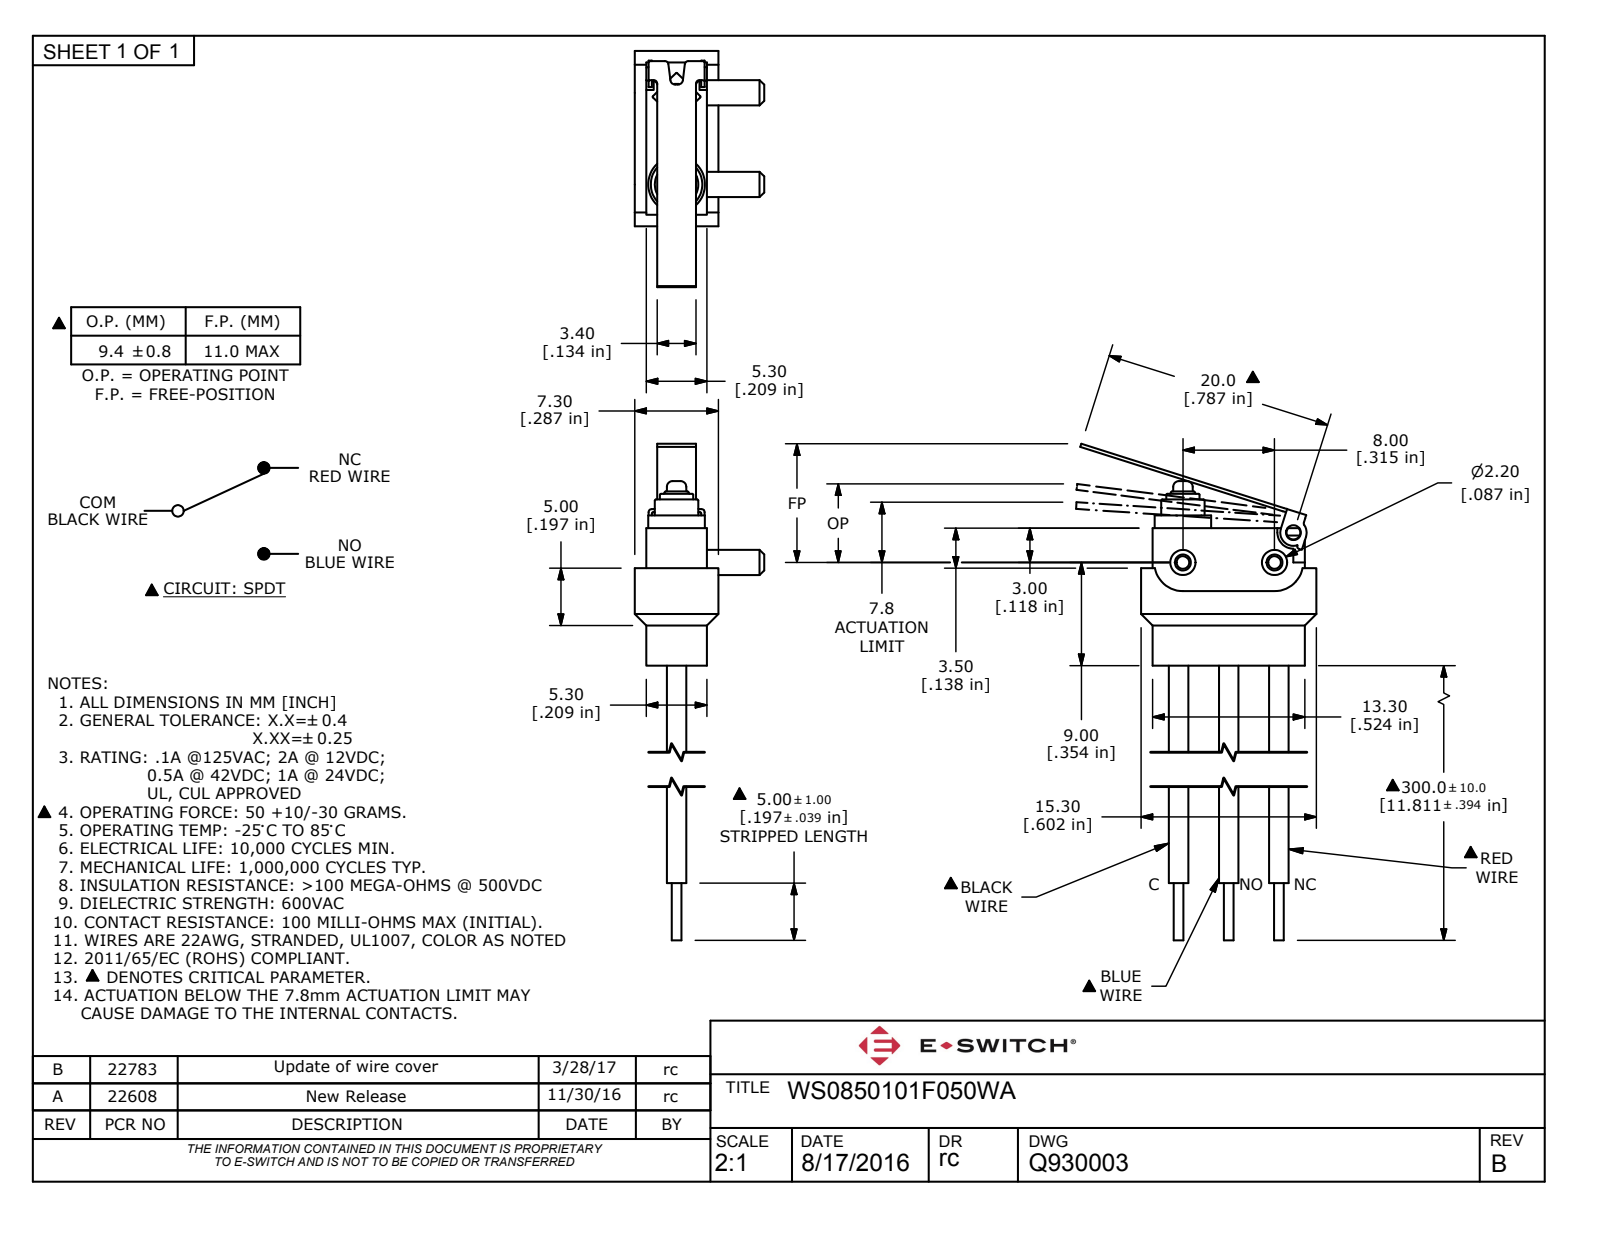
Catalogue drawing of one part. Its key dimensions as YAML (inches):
part_name: "WS0850101F050WA"
step_written_by: "Autodesk Inventor 2012 (CONFIG_CONTROL_DESIGN)"
units: inches
bodies: {solids: 2, faces: 284, planar: 164, cylindrical: 90, other: 30}
overall_size: [12.573, 0.811, 0.445]
volume: 0.178
surface_area: 9.536
round_holes:
  - {diameter: 0.043, count: 2}
  - {diameter: 0.051, count: 1}
  - {diameter: 0.177, count: 1}
round_bosses_or_shafts:
  - {diameter: 0.031, count: 6}
  - {diameter: 0.067, count: 4}
  - {diameter: 0.033, count: 3}
  - {diameter: 0.087, count: 2}
  - {diameter: 0.195, count: 1}
  - {diameter: 0.15, count: 1}
  - {diameter: 0.114, count: 1}
partial_cylinders:
  - {radius: 0.024, count: 7}
  - {radius: 0.012, count: 6}
  - {radius: 0.037, count: 6}
  - {radius: 0.016, count: 3}
  - {radius: 0.004, count: 2}
  - {radius: 0.01, count: 2}
  - {radius: 0.018, count: 2}
  - {radius: 0.098, count: 2}
face_to_face_distances: [0.031, 0.039, 0.217, 0.177, 0.071, 0.209, 0.248, 0.256, 0.146, 0.563]
hole_center_spacings: [0.121, 0.315, 0.393]
